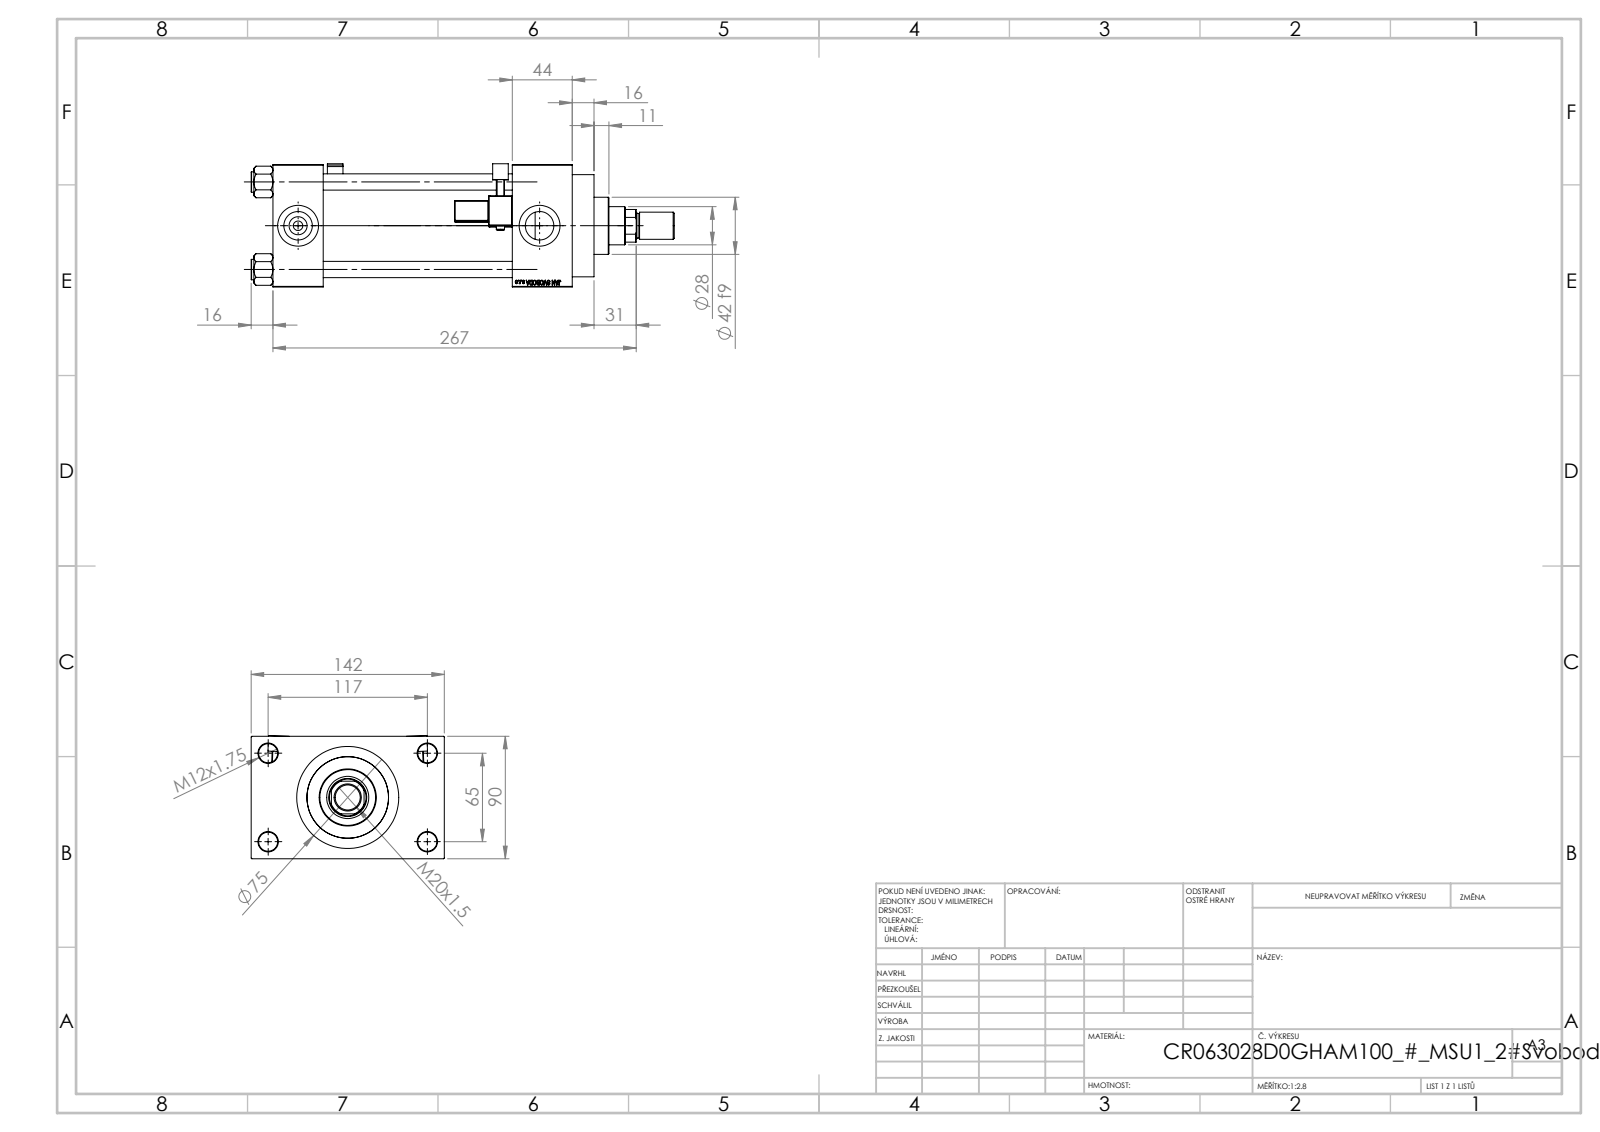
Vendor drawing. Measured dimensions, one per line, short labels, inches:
name: V215CR_MSU; V215_VC_A; V215CR_D_Body; V215CR_D_TYCINKA (+3 more)
written by: SolidWorks 2019 (CONFIG_CONTROL_DESIGN)
unit: in
bodies: 14 solids, 1271 faces (559 planar, 152 cylindrical, 560 other)
size: 12.244 × 5.591 × 3.564
volume: 78.17 in³; area: 414.3 in²
holes: 4× ⌀0.472, 4× ⌀0.551, 2× ⌀0.276, 2× ⌀0.825, 2× ⌀1.181, 1× ⌀0.728, 1× ⌀1.102, 1× ⌀1.22, 1× ⌀1.969, 1× ⌀2.362, 1× ⌀2.48
bosses: 4× ⌀0.591, 2× ⌀0.236, 1× ⌀2.953, 1× ⌀2.717, 1× ⌀1.654, 1× ⌀0.787, 1× ⌀0.709
rounds: 48× R0.02, 2× R0.039, 2× R0.098, 2× R0.157, 1× R0.531
face distances: 3.543, 5.472, 1.457, 6.929, 8.661, 7.205, 1.732, 1.024, 4.567, 0.63
hole spacings: 1.037, 1.79, 2.531, 2.635, 2.748, 3.569, 4.383, 2.559
